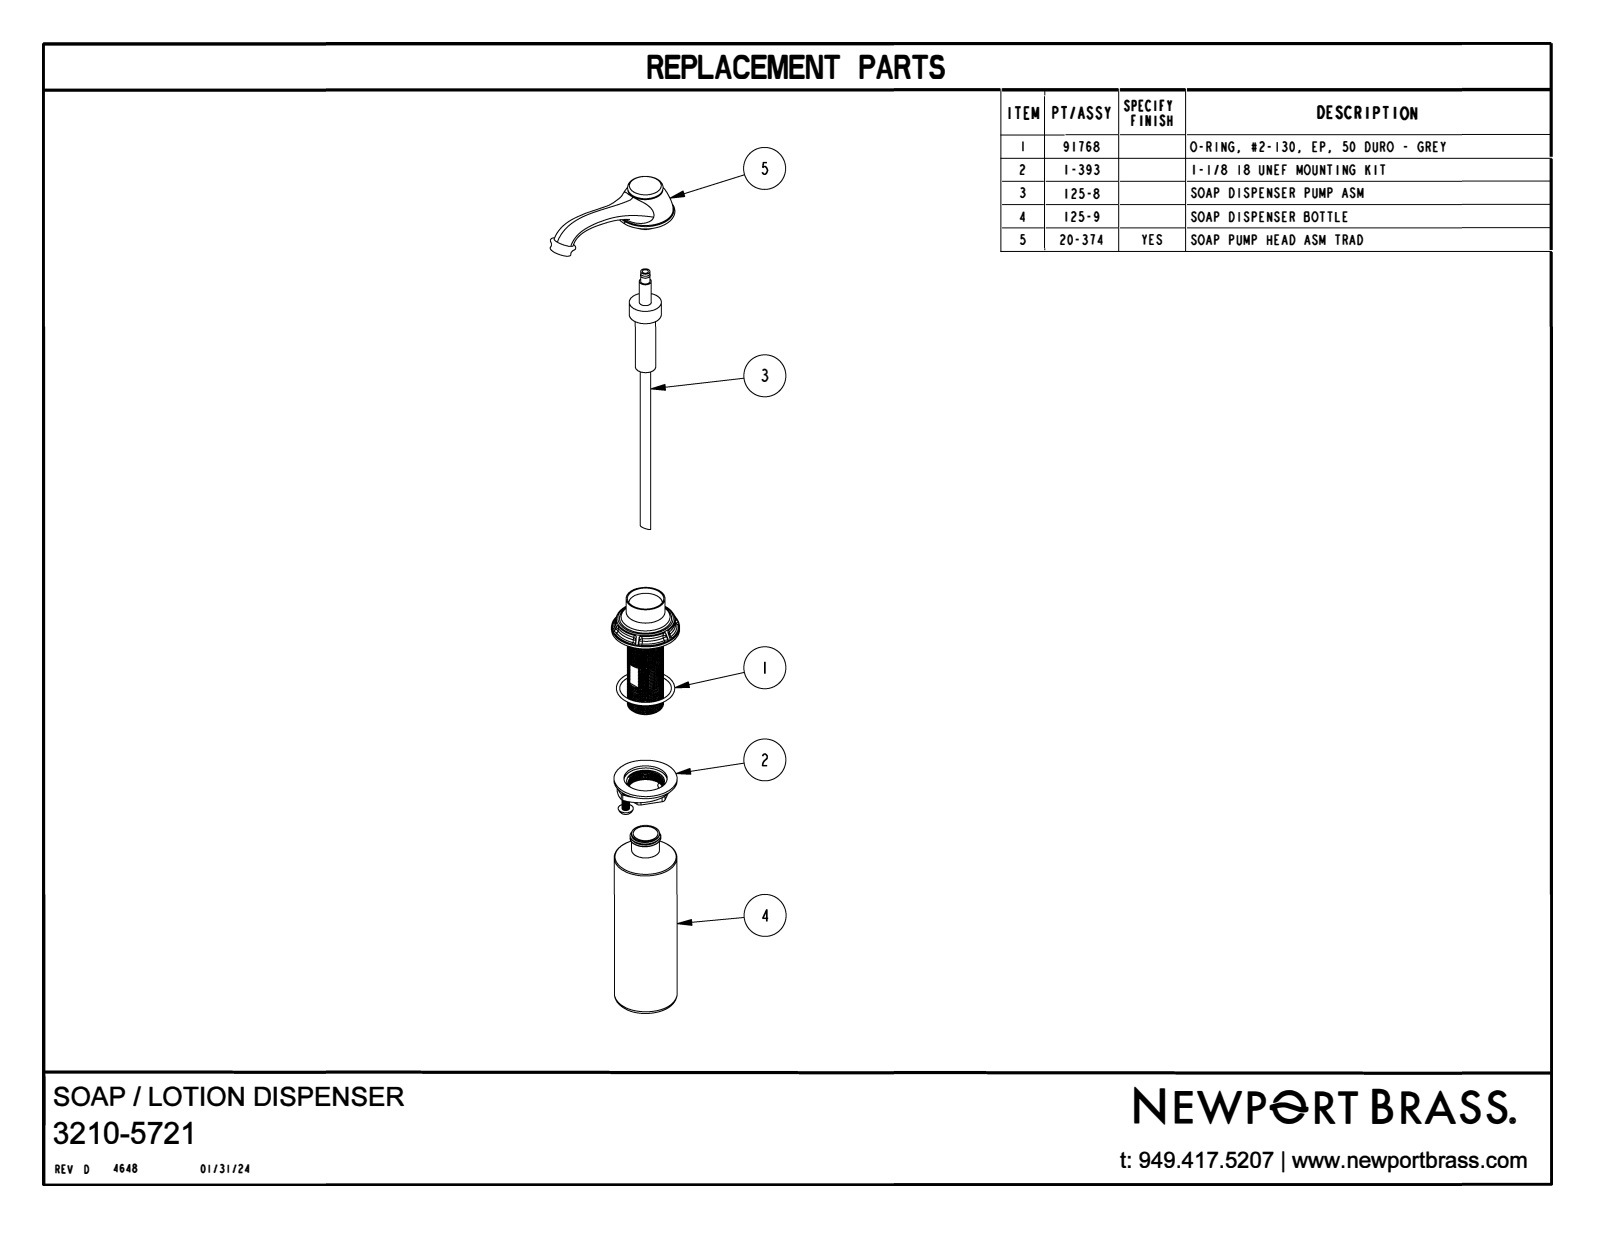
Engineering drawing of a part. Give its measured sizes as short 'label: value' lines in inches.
name: 3210-5721
written by: CREO PARAMETRIC BY PTC INC, 2018400 (CONFIG_CONTROL_DESIGN)
unit: in
bodies: 1 solid, 186 faces (10 planar, 10 cylindrical, 166 other)
size: 5.111 × 2.394 × 2.125
volume: 4.934 in³; area: 24.22 in²
bosses: 1× ⌀2.125, 1× ⌀1.21
rounds: 1× R0.92
face distances: 1.171, 0.425, 0.746, 0.1, 0.325, 1.071
